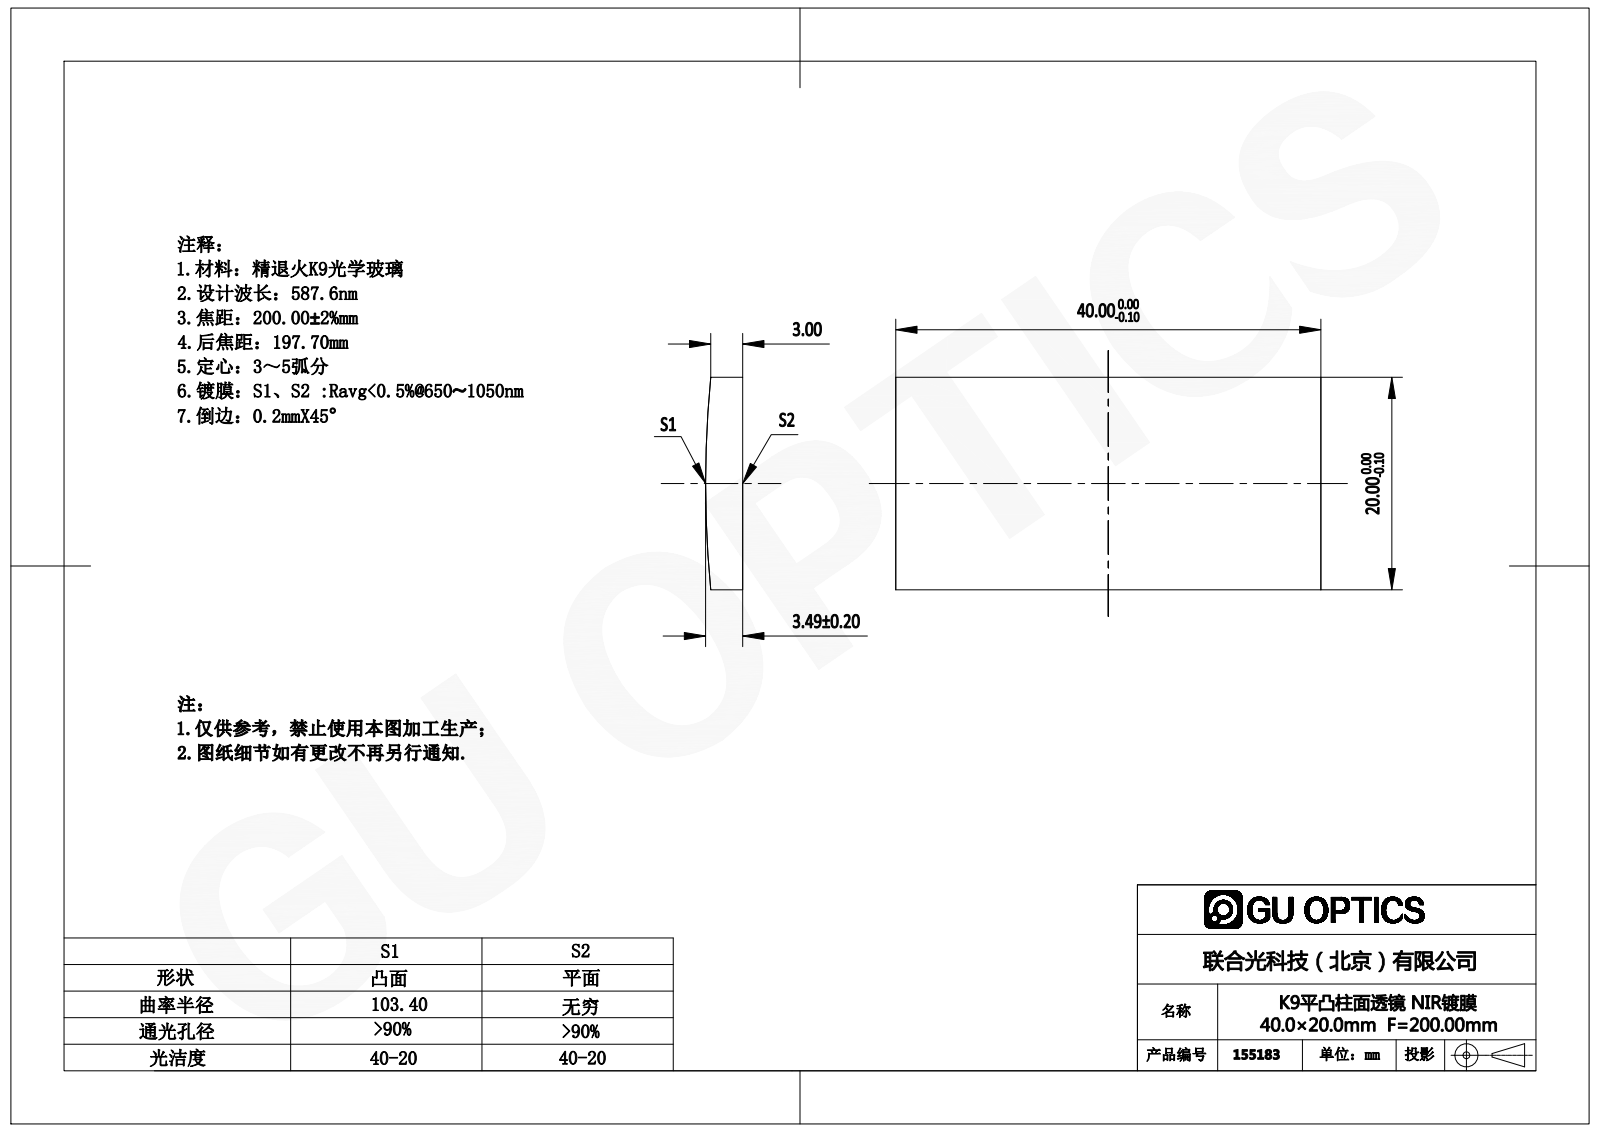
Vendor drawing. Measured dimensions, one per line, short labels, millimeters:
name: 155051
written by: SolidWorks 2016 (AUTOMOTIVE_DESIGN)
unit: mm
bodies: 1 solid, 6 faces (5 planar, 1 cylindrical, 0 other)
size: 40 × 20 × 3.49
volume: 2 663 mm³; area: 1 975 mm²
rounds: 1× R103.4
face distances: 20, 40
